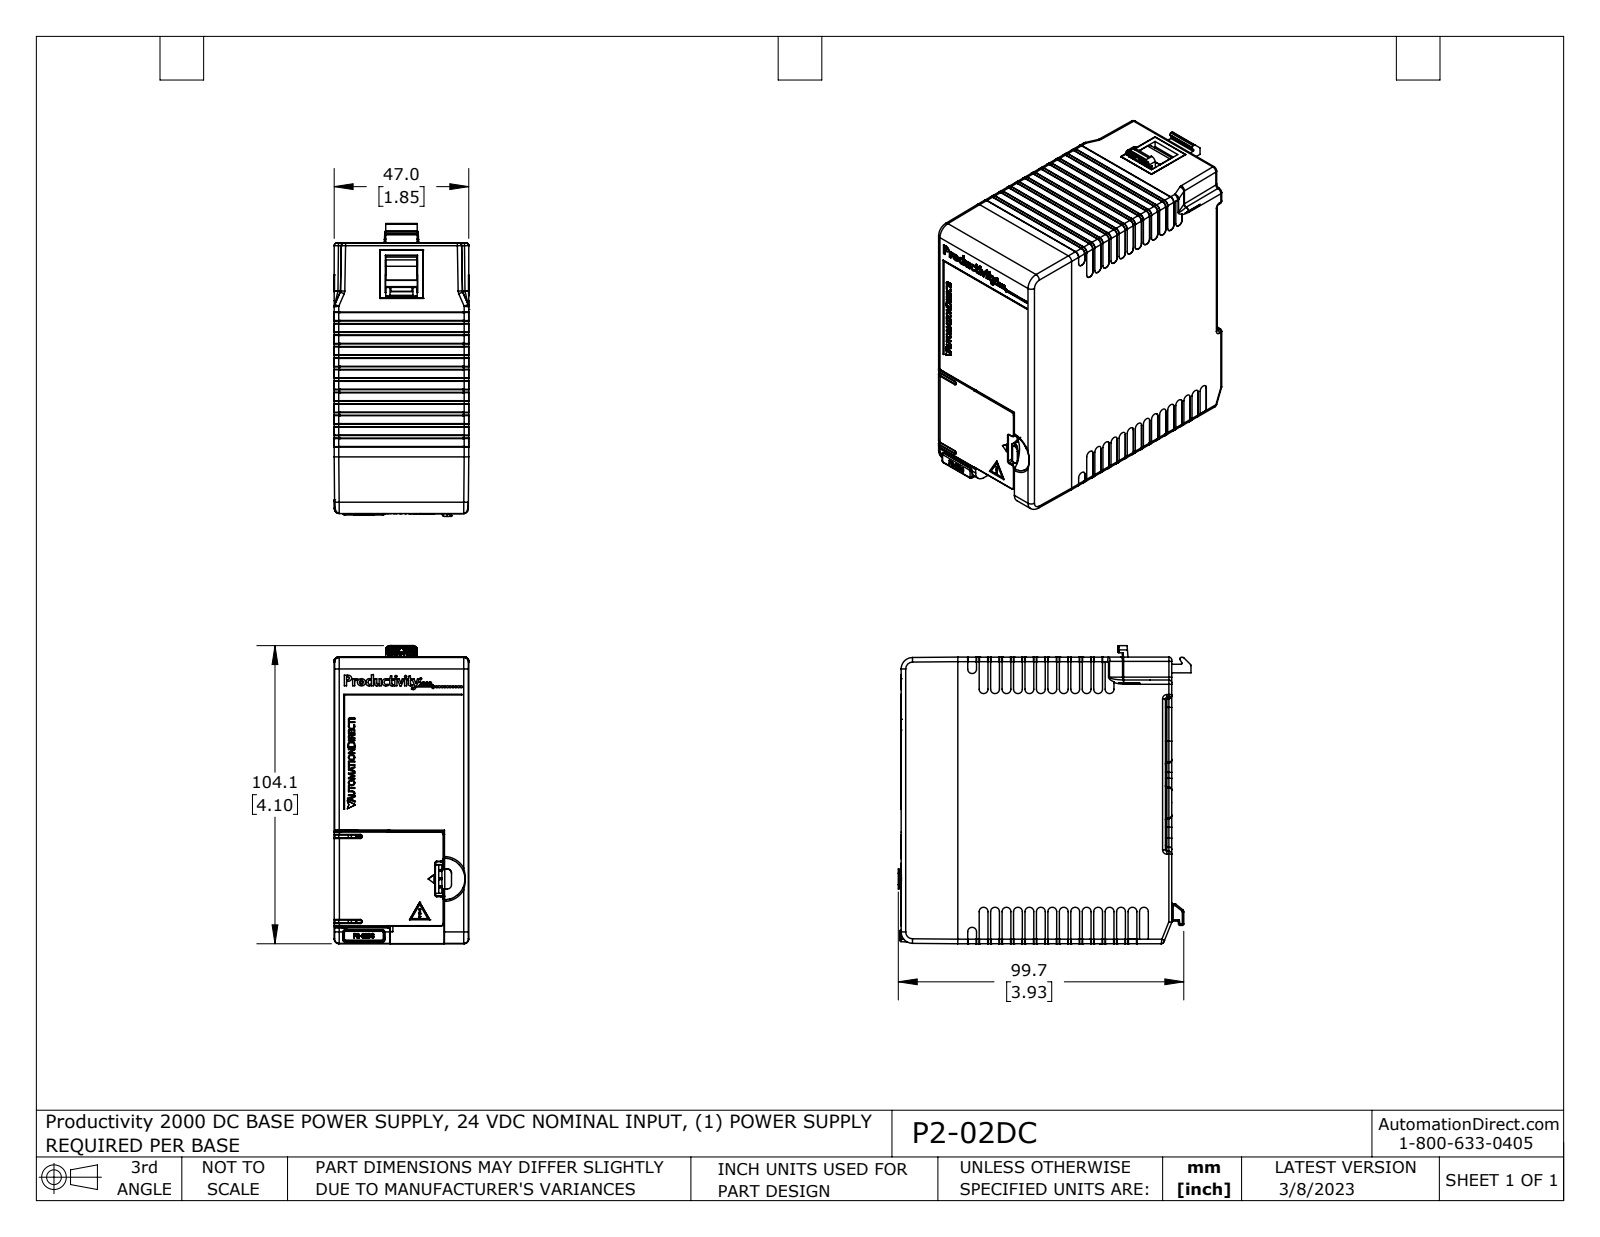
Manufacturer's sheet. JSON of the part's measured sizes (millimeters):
{"part_name": "P2-01AC DIN Coord sk1vx BcX fxt sr1", "step_written_by": "SolidWorks 2021 (AUTOMOTIVE_DESIGN)", "units": "millimeters", "bodies": {"solids": 5, "faces": 3381, "planar": 1676, "cylindrical": 626, "other": 1079}, "overall_size": [104.1, 102.2, 47], "volume_mm3": 338200, "surface_area_mm2": 77870, "round_holes": [[1, 4], [1.2, 4], [1.7, 4], [3.2, 3], [3.3, 2], [3.4, 2], [4.2, 2], [1.2, 1], [2, 1], [2.2, 1]], "round_bosses_or_shafts": [[5.6, 2], [2.8, 2], [10.6, 1], [2.5, 1]], "partial_cylinders_radius": [[0.5, 169], [1, 81], [0.2, 64], [1.5, 15], [1.6, 10], [2, 9], [0.4, 6], [3, 6]], "face_to_face_distances": [1.6, 45.4, 1.5, 83.3, 63.5, 19.8, 46.9, 47, 11.2, 74.7], "hole_center_spacings": [7.5, 5.1, 7.6, 10.2, 10.6, 15.2, 15.5, 20.6]}
